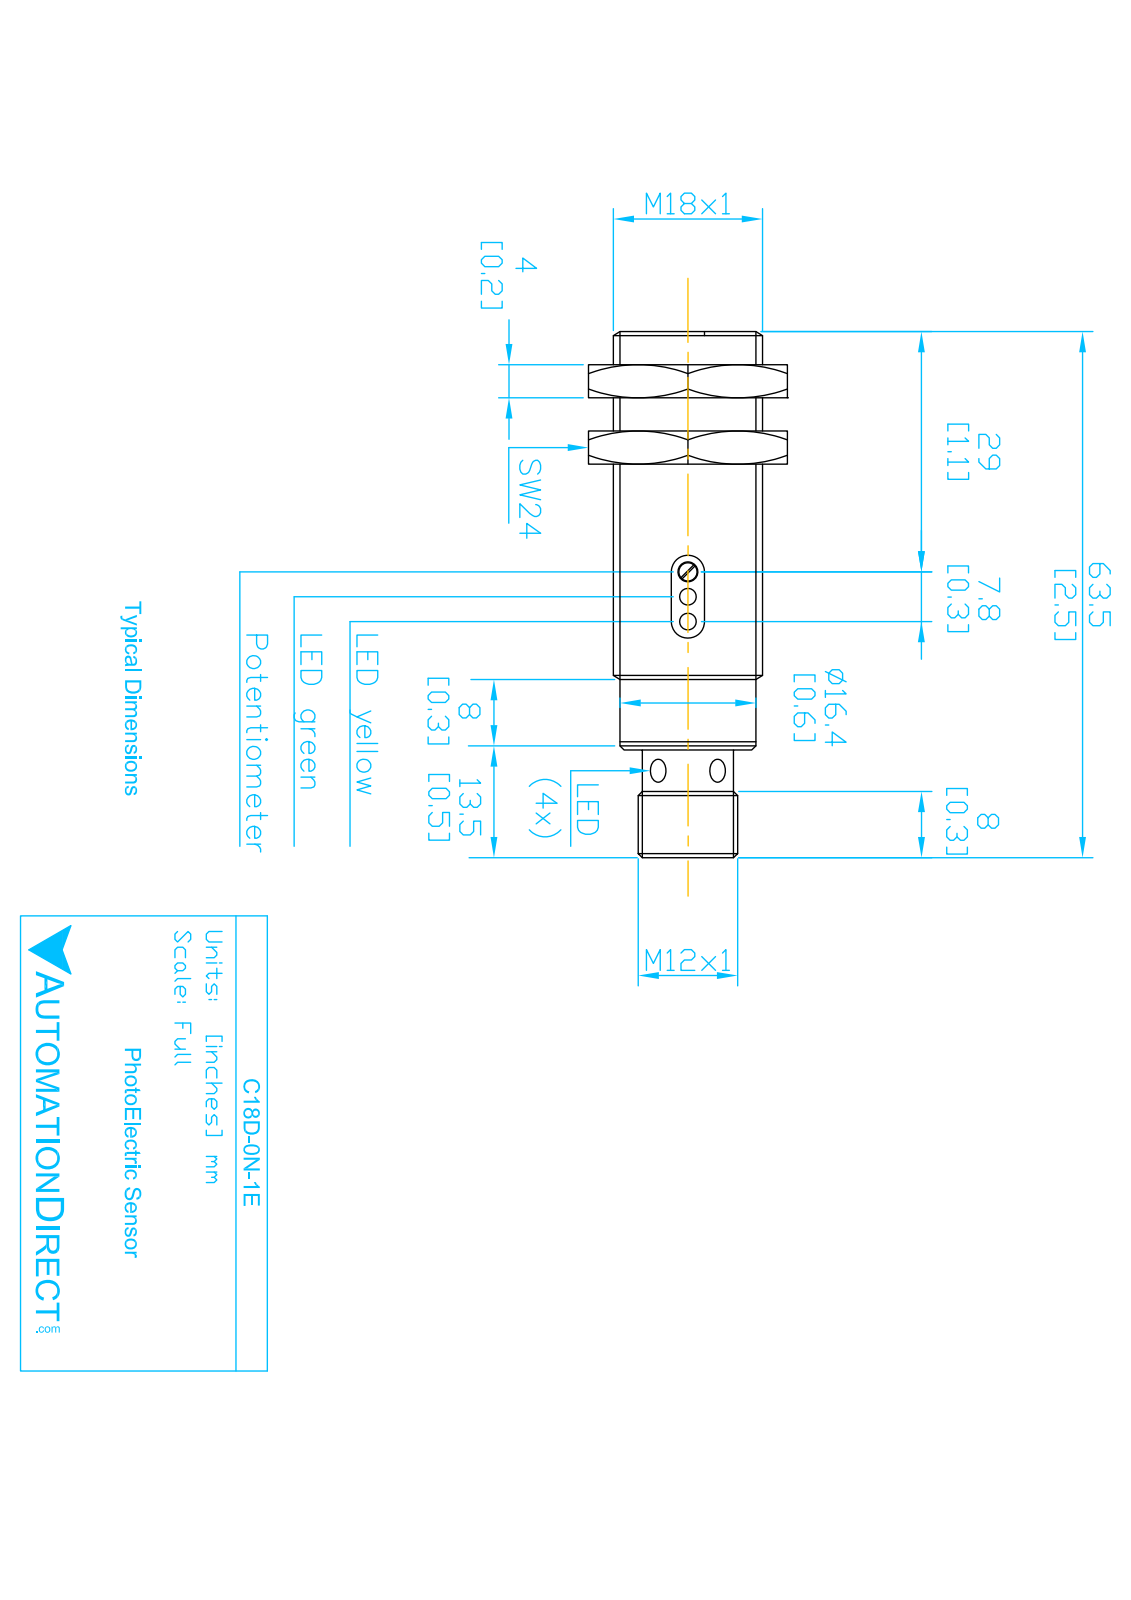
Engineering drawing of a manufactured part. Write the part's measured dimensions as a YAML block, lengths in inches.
part_name: "C18D-0N-1E"
step_written_by: "SolidWorks 2017 (AUTOMOTIVE_DESIGN)"
units: inches
bodies: {solids: 3, faces: 63, planar: 15, cylindrical: 29, other: 19}
overall_size: [2.5, 0.709, 0.709]
volume: 0.823
surface_area: 7.992
round_holes:
  - {diameter: 0.118, count: 2}
  - {diameter: 0.335, count: 1}
round_bosses_or_shafts:
  - {diameter: 0.04, count: 4}
  - {diameter: 0.709, count: 1}
  - {diameter: 0.646, count: 1}
  - {diameter: 0.619, count: 1}
  - {diameter: 0.459, count: 1}
  - {diameter: 0.415, count: 1}
partial_cylinders:
  - {radius: 0.02, count: 3}
  - {radius: 0.202, count: 1}
face_to_face_distances: [1.988, 0.1, 1.888, 0.092, 1.98, 2.158, 2.15, 2.058, 0.17, 2.5]
